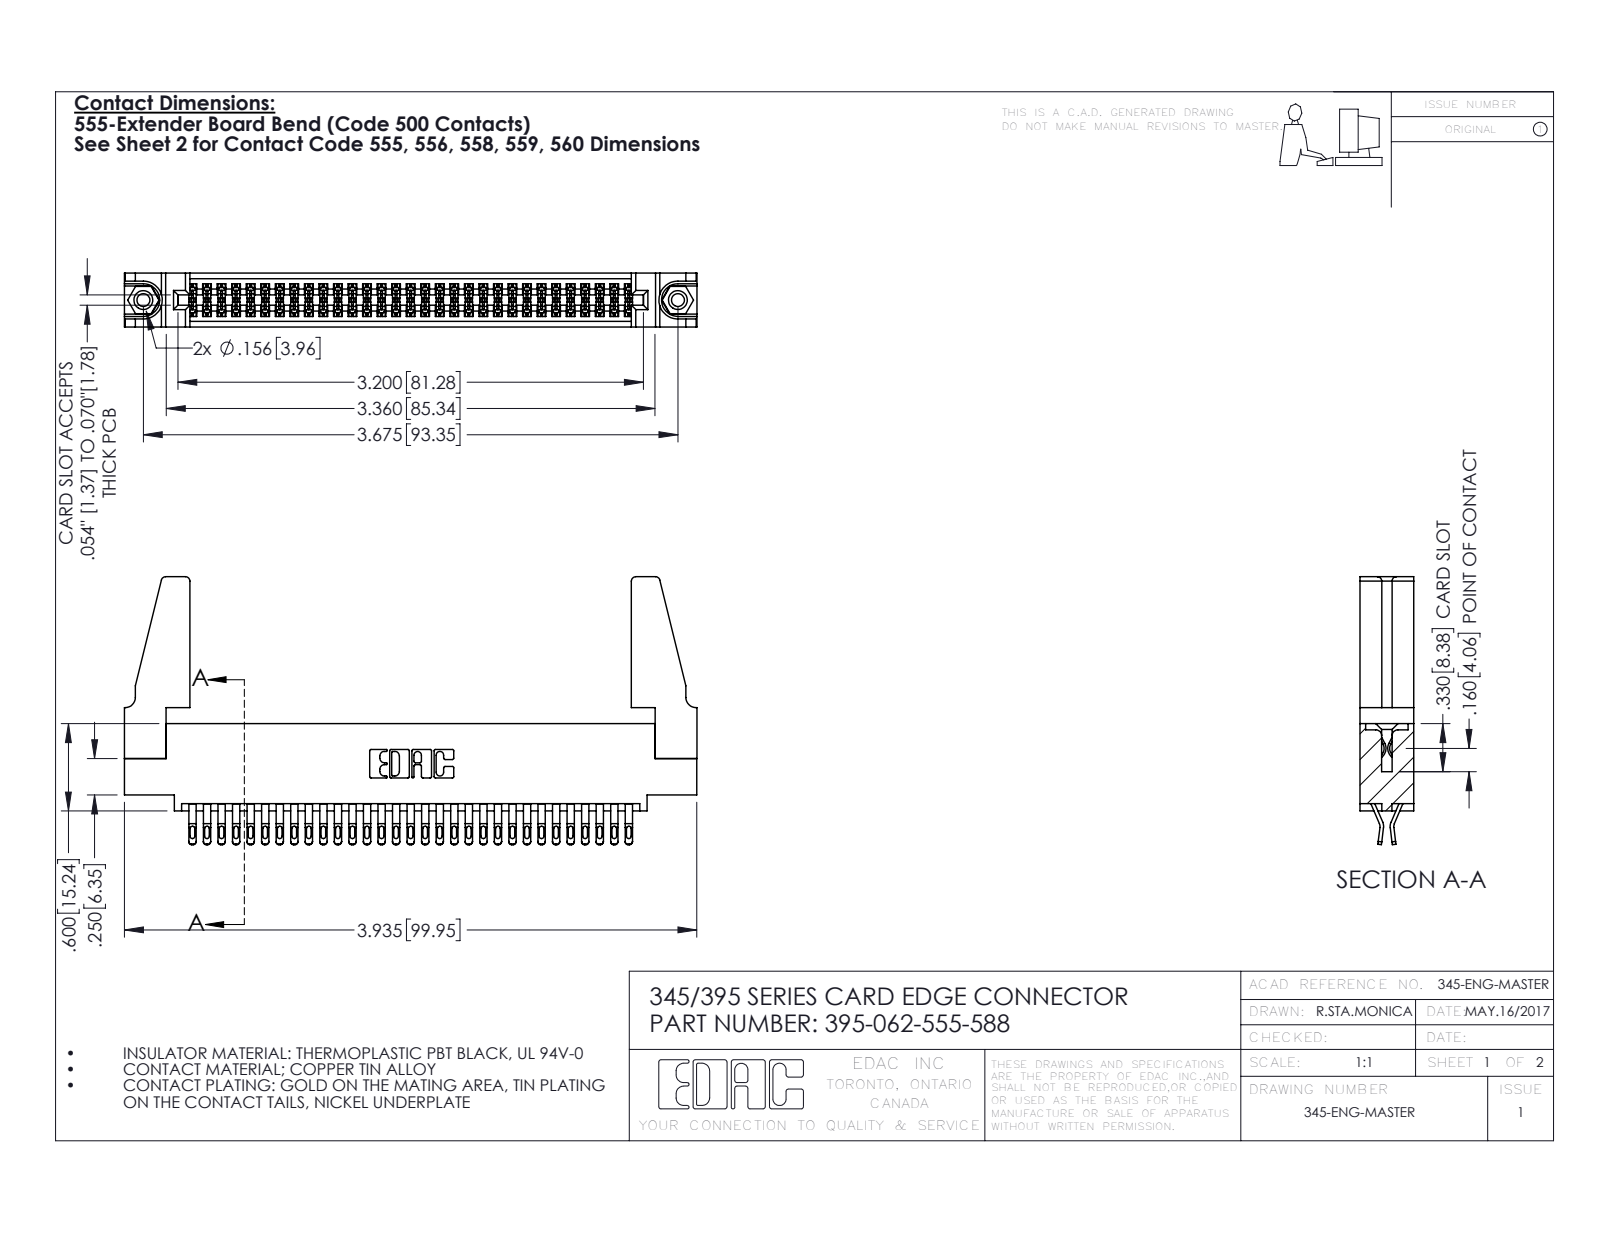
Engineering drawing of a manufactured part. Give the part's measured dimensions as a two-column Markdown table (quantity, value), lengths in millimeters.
| quantity | value |
| --- | --- |
| part name | 345 Part_0.110 Offset - 0.156 Dia-TH; 345-250-001_345-250-001-102; 395-062-555-588; 345-220-078_345-220-088 (+1 more) |
| STEP written by | SolidWorks 2016 (CONFIG_CONTROL_DESIGN) |
| units | millimeters |
| bodies | 67 solids, 3726 faces (2078 planar, 1632 cylindrical, 16 other) |
| overall size | 100 × 46.8 × 9.4 |
| volume | 13 000 mm³ |
| surface area | 17 990 mm² |
| round holes (diameter × count) | 2.3 × 2, 3.2 × 2, 4 × 2, 1.6 × 1 |
| round bosses / shafts (diameter × count) | 3.9 × 2 |
| partial cylindrical surfaces (radius × count) | 0.4 × 155, 0.5 × 124, 0.2 × 93, 0.3 × 22, 0.8 × 8, 0.2 × 6, 0.8 × 6, 0.7 × 3 |
| main face-to-face distances | 1.8, 7.6, 9.4, 0.6, 5.1, 2.5, 6.9, 5.7, 4.4, 3.8 |
| hole center spacings | 6.9, 87.4, 93.3 |
